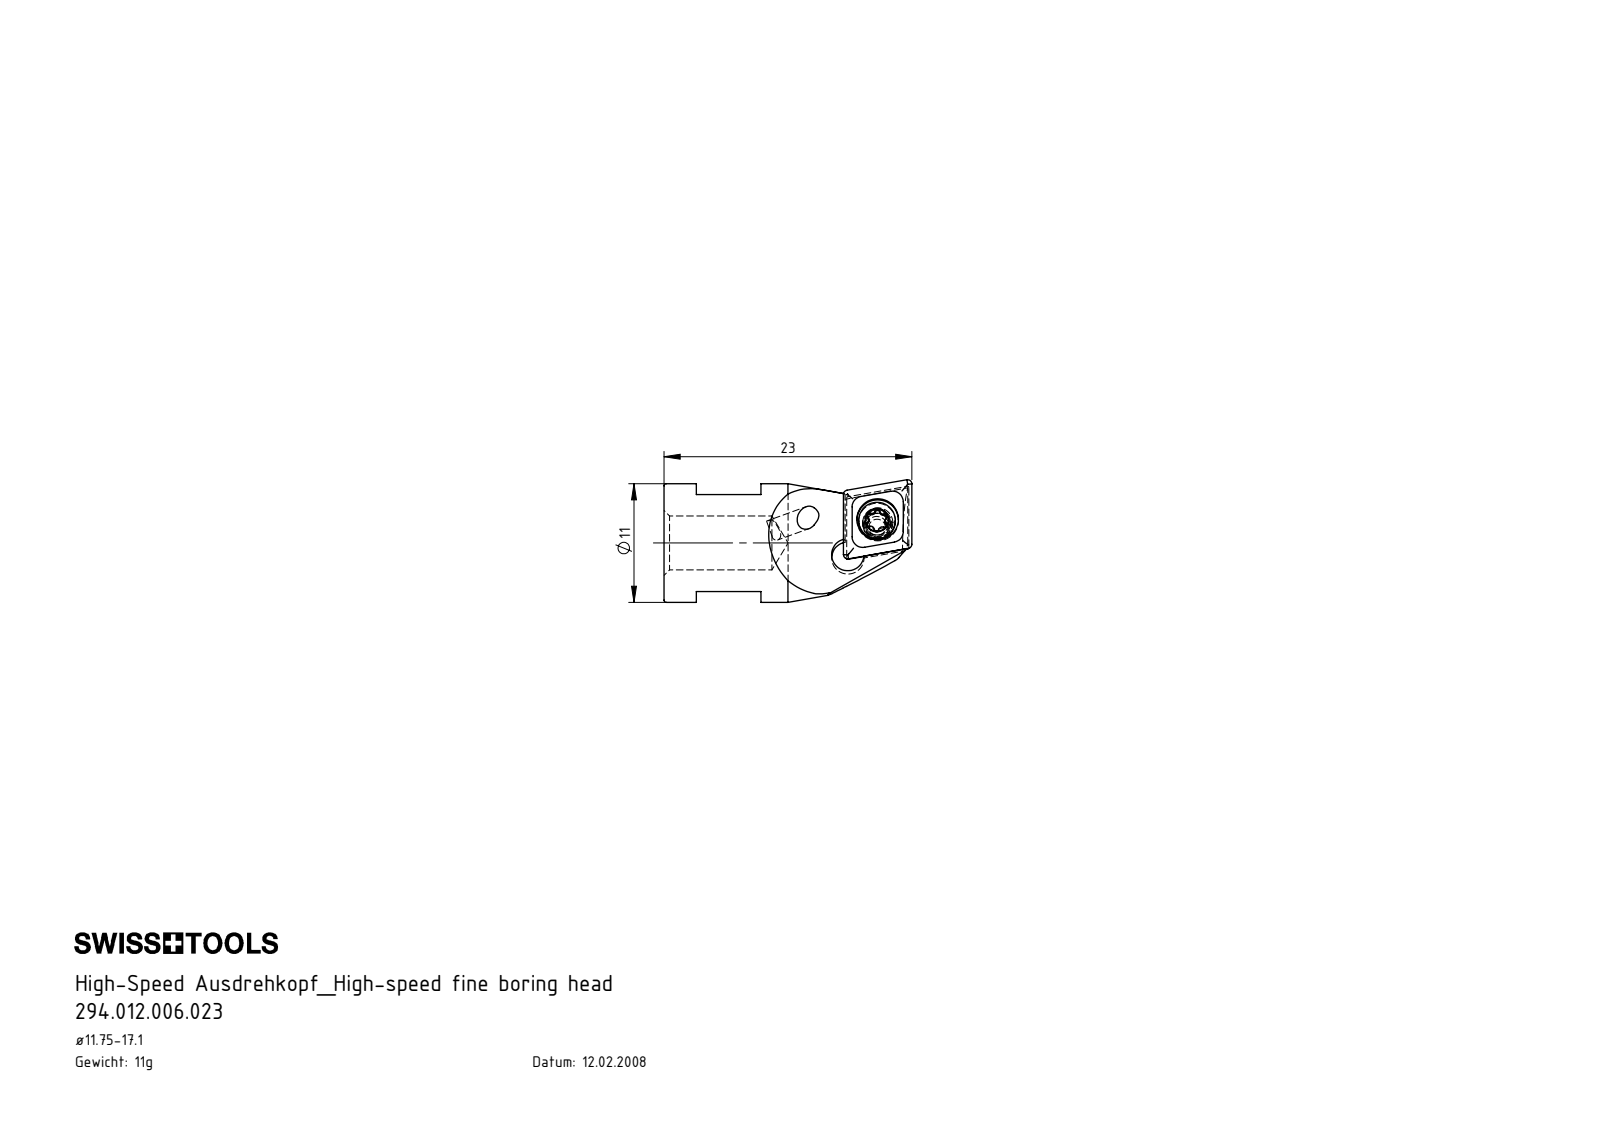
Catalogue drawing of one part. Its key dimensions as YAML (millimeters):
part_name: "HS6.A12.K11.023; WCA-ER2.001.005_A; HS6-A12.K11.023_B; CCMT060204"
step_written_by: "SolidWorks 2017 (AUTOMOTIVE_DESIGN)"
units: millimeters
bodies: {solids: 3, faces: 123, planar: 34, cylindrical: 35, other: 54}
overall_size: [23, 11.38, 11.02]
volume: 1302
surface_area: 1225
round_holes:
  - {diameter: 2, count: 1}
  - {diameter: 2.05, count: 1}
  - {diameter: 2.8, count: 1}
  - {diameter: 3.85, count: 1}
  - {diameter: 5, count: 1}
round_bosses_or_shafts:
  - {diameter: 11, count: 1}
  - {diameter: 3.4, count: 1}
  - {diameter: 2.5, count: 1}
partial_cylinders:
  - {radius: 0.21, count: 6}
  - {radius: 0.36, count: 5}
  - {radius: 0.36, count: 1}
  - {radius: 1.4, count: 1}
  - {radius: 1.5, count: 1}
  - {radius: 2, count: 1}
face_to_face_distances: [8.99, 2.28, 2.38, 3, 9, 6, 16.8, 13.8, 7.8, 1.48]
